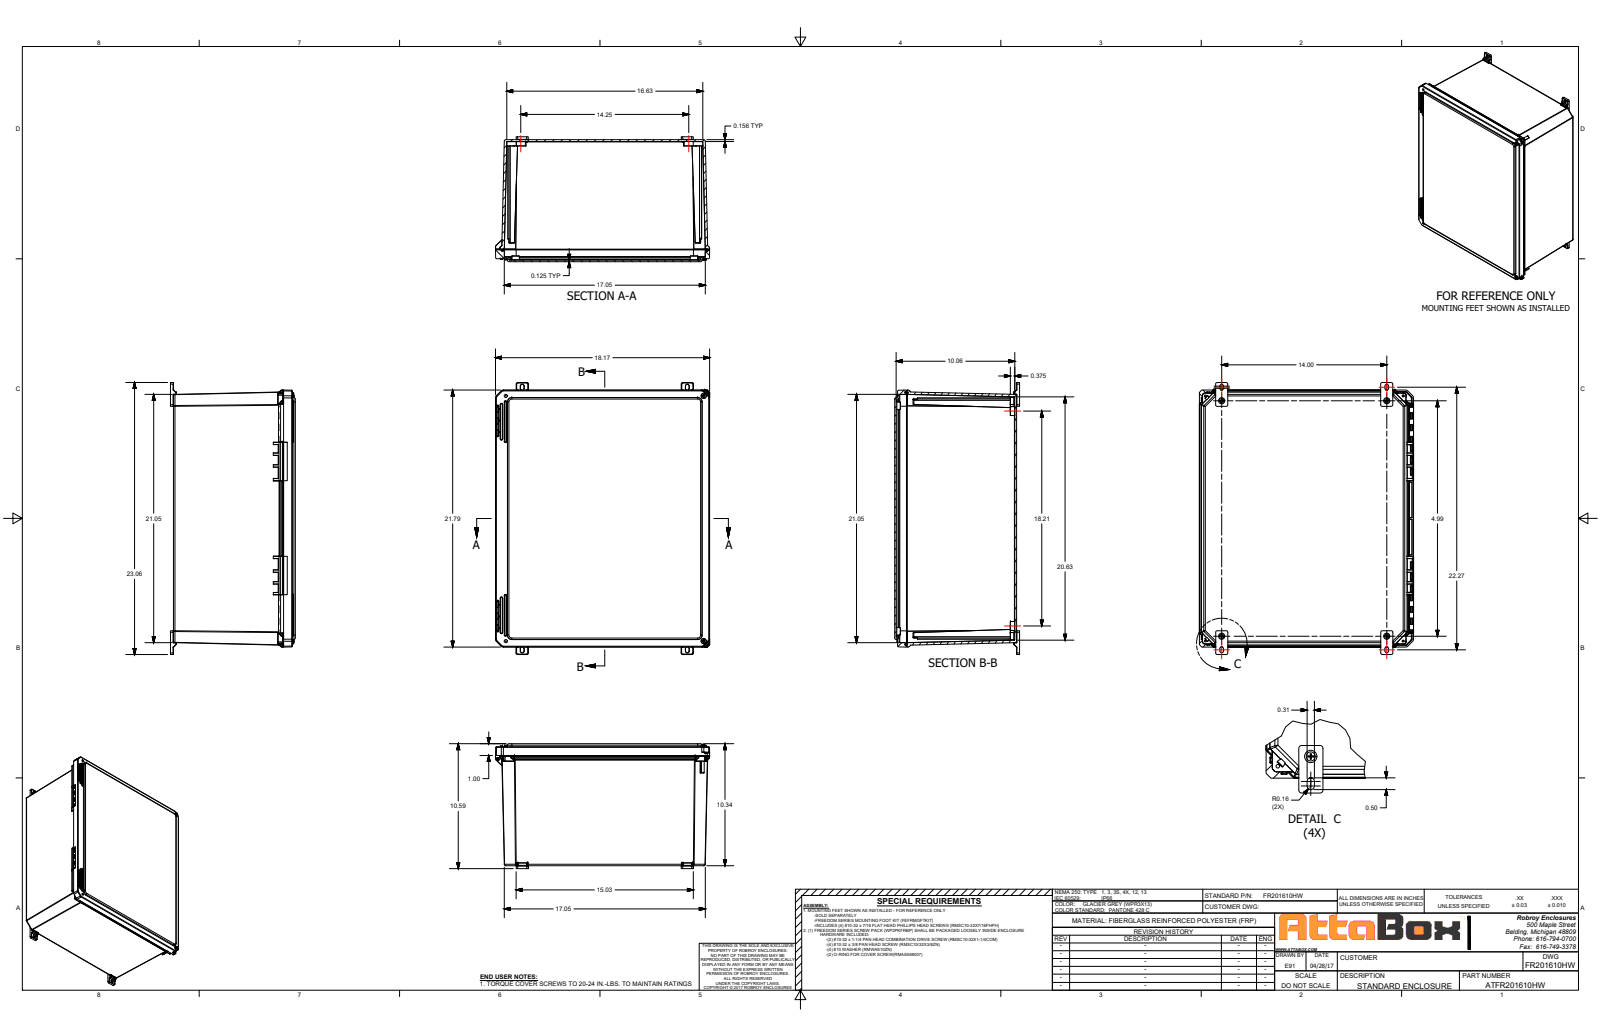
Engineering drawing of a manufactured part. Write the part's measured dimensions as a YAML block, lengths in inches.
part_name: "FR201610HW"
step_written_by: "SolidWorks 2021 (AUTOMOTIVE_DESIGN)"
units: inches
bodies: {solids: 7, faces: 2131, planar: 672, cylindrical: 830, other: 629}
overall_size: [21.791, 18.166, 10.341]
volume: 284.6
surface_area: 3168
round_holes:
  - {diameter: 0.152, count: 8}
  - {diameter: 0.252, count: 4}
  - {diameter: 0.253, count: 4}
  - {diameter: 0.219, count: 2}
  - {diameter: 0.227, count: 2}
  - {diameter: 0.313, count: 2}
  - {diameter: 0.137, count: 1}
round_bosses_or_shafts:
  - {diameter: 0.45, count: 2}
  - {diameter: 0.435, count: 2}
  - {diameter: 0.199, count: 2}
  - {diameter: 0.135, count: 1}
partial_cylinders:
  - {radius: 0.01, count: 173}
  - {radius: 0.005, count: 88}
  - {radius: 0.02, count: 49}
  - {radius: 0.03, count: 44}
  - {radius: 0.03, count: 24}
  - {radius: 0.09, count: 24}
  - {radius: 0.096, count: 24}
  - {radius: 0.125, count: 22}
face_to_face_distances: [0.125, 0.156, 10.185, 10.341, 10.217, 10.061, 0.21, 0.212, 0.25, 0.125]
hole_center_spacings: [19.56, 19.979, 20.42, 24.937, 0.862, 1.172, 1.795, 14.698]
